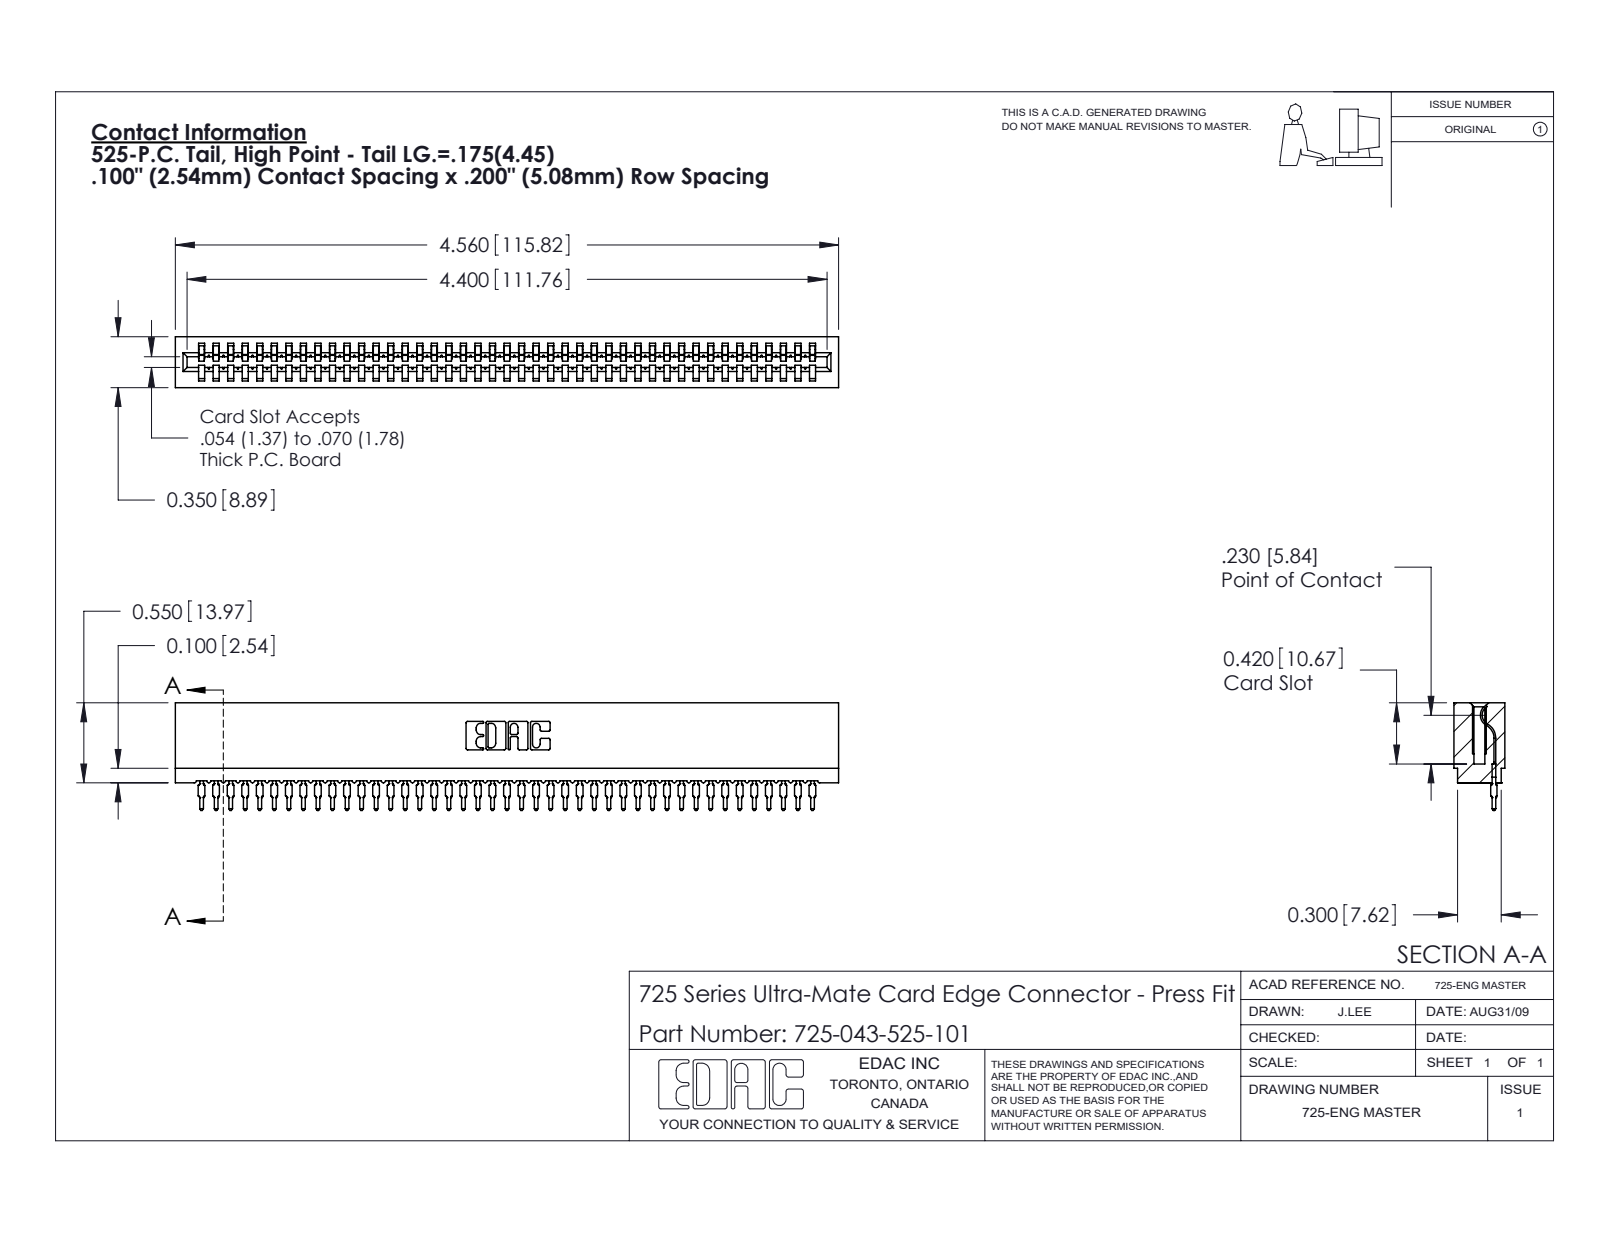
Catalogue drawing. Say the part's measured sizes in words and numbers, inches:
The part is named "725 Part_Insulator Option - 01; 745-292-001_525; 725-043-525-101". Its 3-D file was written by "SolidWorks 2020 (CONFIG_CONTROL_DESIGN)". It is 44 solids with 4911 faces: 2936 planar, 857 cylindrical and 1118 other. Overall it measures 4.56 by 0.741 by 0.35 inches. Its volume is 0.534 cubic inches and its surface area 25.99 square inches. Partial cylindrical surfaces (rounded edges, fillets, slot ends): 86 of radius 0.015, 86 of radius 0.021, 22 of radius 0.01, 6 of radius 0.007, 6 of radius 0.031, 4 of radius 0.005, 4 of radius 0.011, 3 of radius 0.026. The main face-to-face distances are 0.35, 0.212, 0.138, 0.045, 0.305, 0.093, 0.167, 0.063, 0.287, 0.076.
